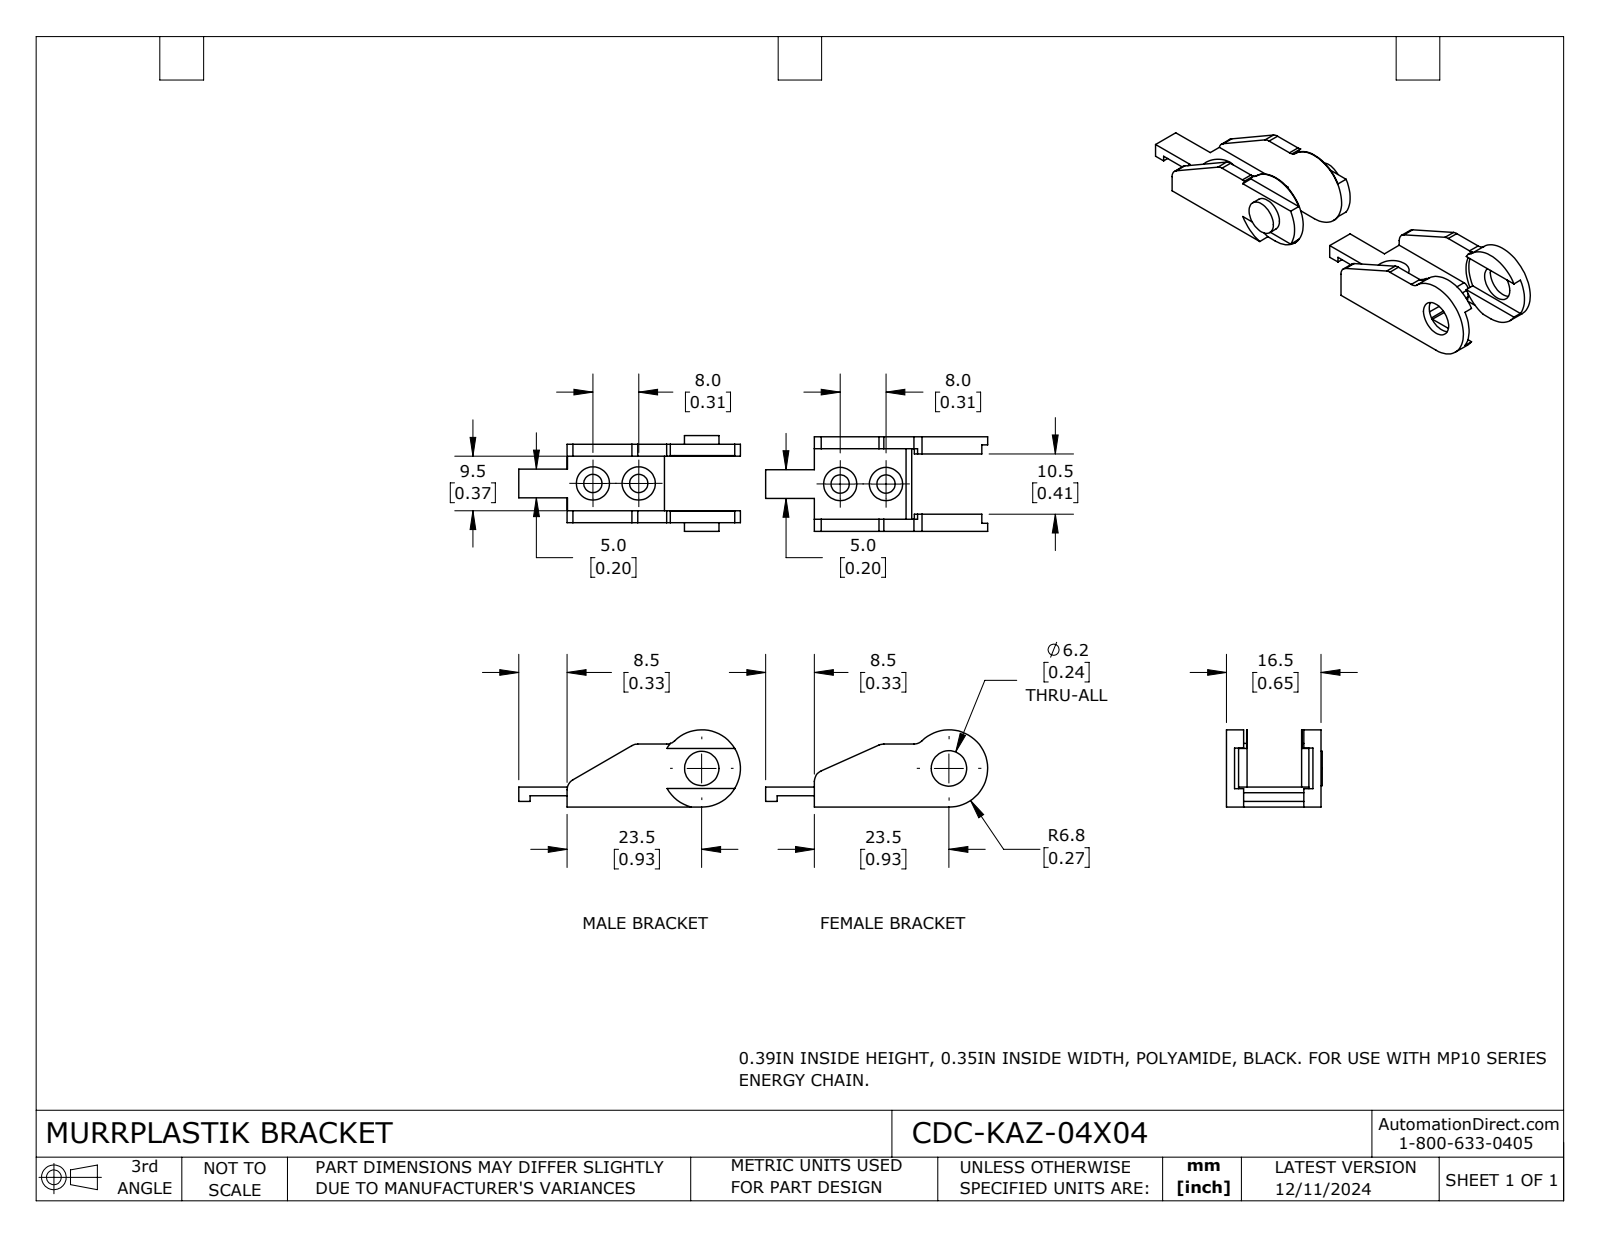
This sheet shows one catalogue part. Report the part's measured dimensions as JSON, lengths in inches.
{"part_name": "CDC-KAZ-04X04", "step_written_by": "SolidWorks 2024 (AUTOMOTIVE_DESIGN)", "units": "inches", "bodies": {"solids": 2, "faces": 96, "planar": 56, "cylindrical": 36, "other": 4}, "overall_size": [3.224, 0.657, 0.531], "volume_in3": 0.218, "surface_area_in2": 6.447, "round_holes": [[0.126, 4], [0.244, 1]], "round_bosses_or_shafts": [[0.236, 1]], "partial_cylinders_radius": [[0.079, 6], [0.039, 2], [0.266, 2], [0.276, 2]], "face_to_face_distances": [0.083, 0.457, 0.059, 0.138, 0.516, 0.508, 0.051, 0.539, 0.65, 0.142], "hole_center_spacings": [0.315, 1.7, 1.385, 2.015]}
